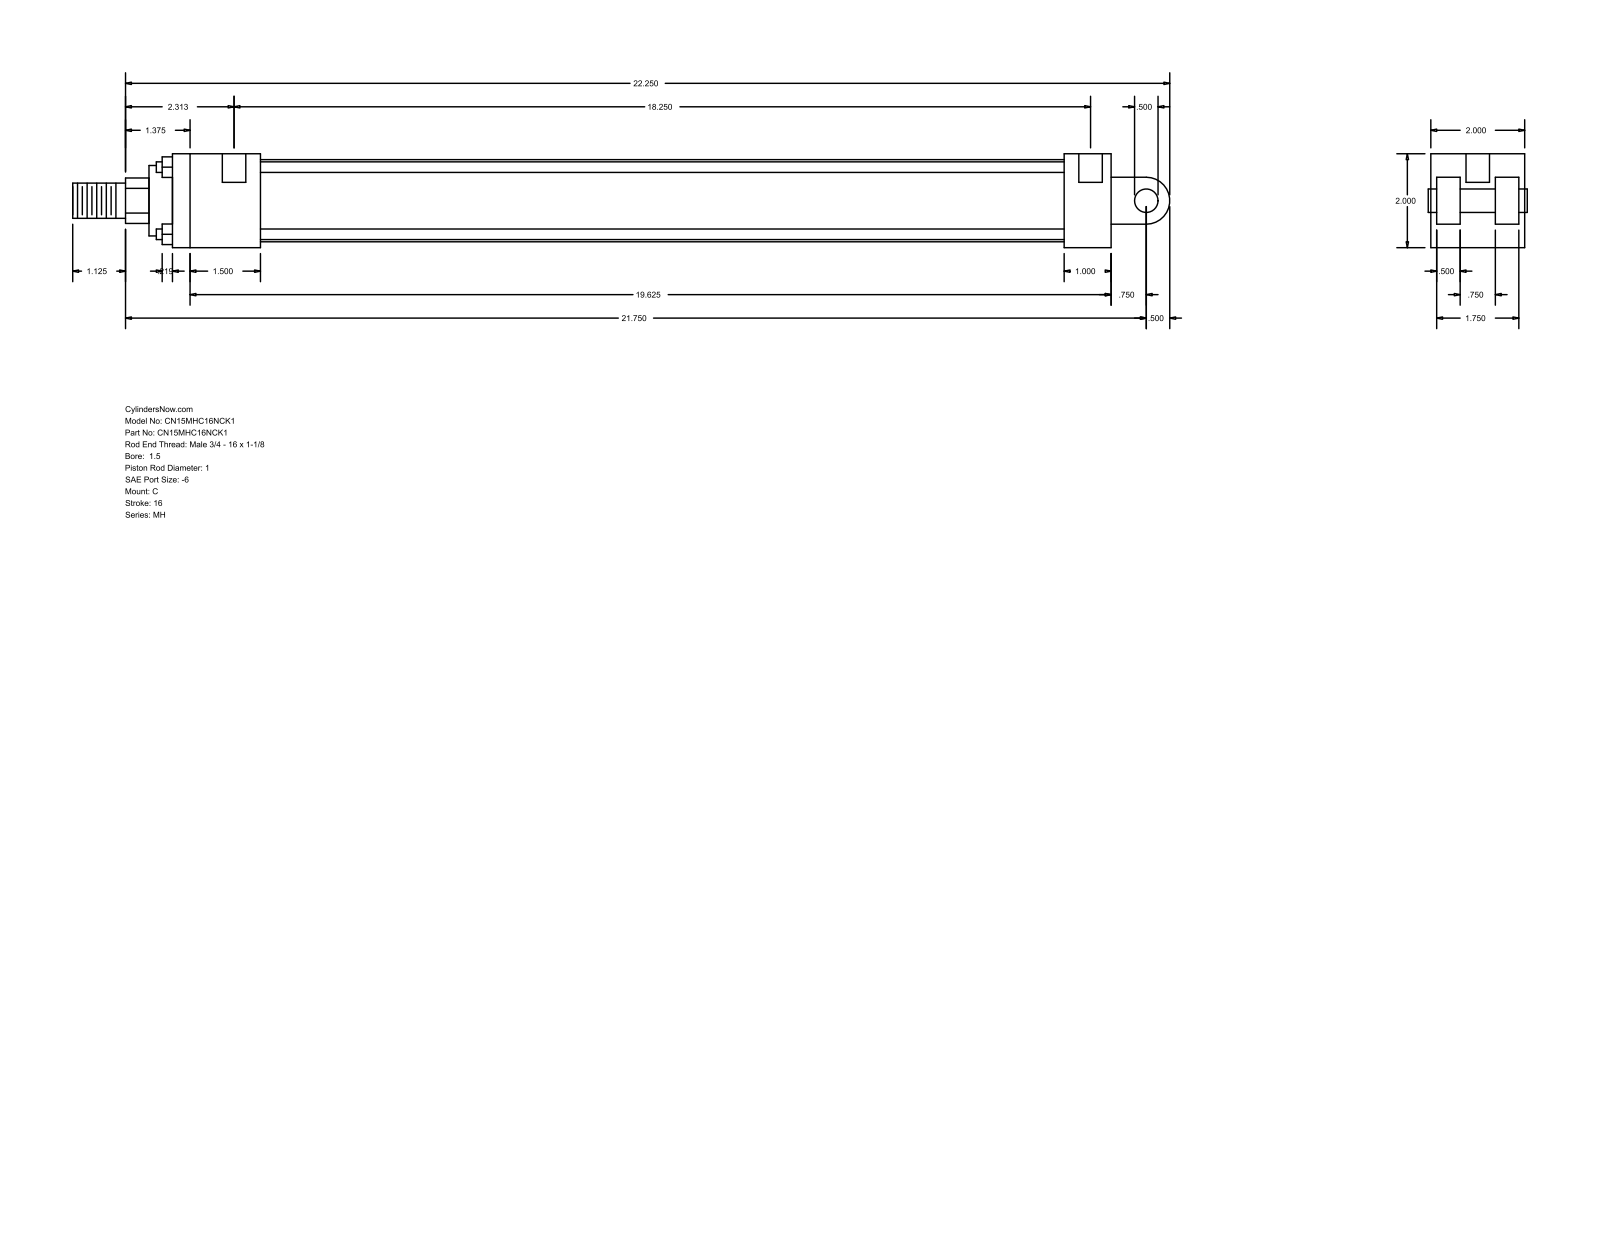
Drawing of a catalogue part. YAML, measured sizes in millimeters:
part_name: "MH_C__0150_1"
step_written_by: "GSSL Pune (CONFIG_CONTROL_DESIGN)"
units: millimeters
bodies: {solids: 0, faces: 99, planar: 70, cylindrical: 29, other: 0}
overall_size: [593.73, 50.8, 50.8]
round_holes:
  - {diameter: 5.56, count: 4}
  - {diameter: 12.7, count: 2}
round_bosses_or_shafts:
  - {diameter: 5.71, count: 4}
  - {diameter: 44.45, count: 1}
  - {diameter: 38.1, count: 1}
  - {diameter: 25.4, count: 1}
  - {diameter: 19.05, count: 1}
  - {diameter: 12.7, count: 1}
partial_cylinders:
  - {radius: 12.29, count: 1}
  - {radius: 12.7, count: 1}
face_to_face_distances: [50.8, 12.7, 47.63, 25.4, 3.17, 15.87, 34.93, 31.76, 508, 38.1]
hole_center_spacings: [466.73, 3.18, 463.55]
